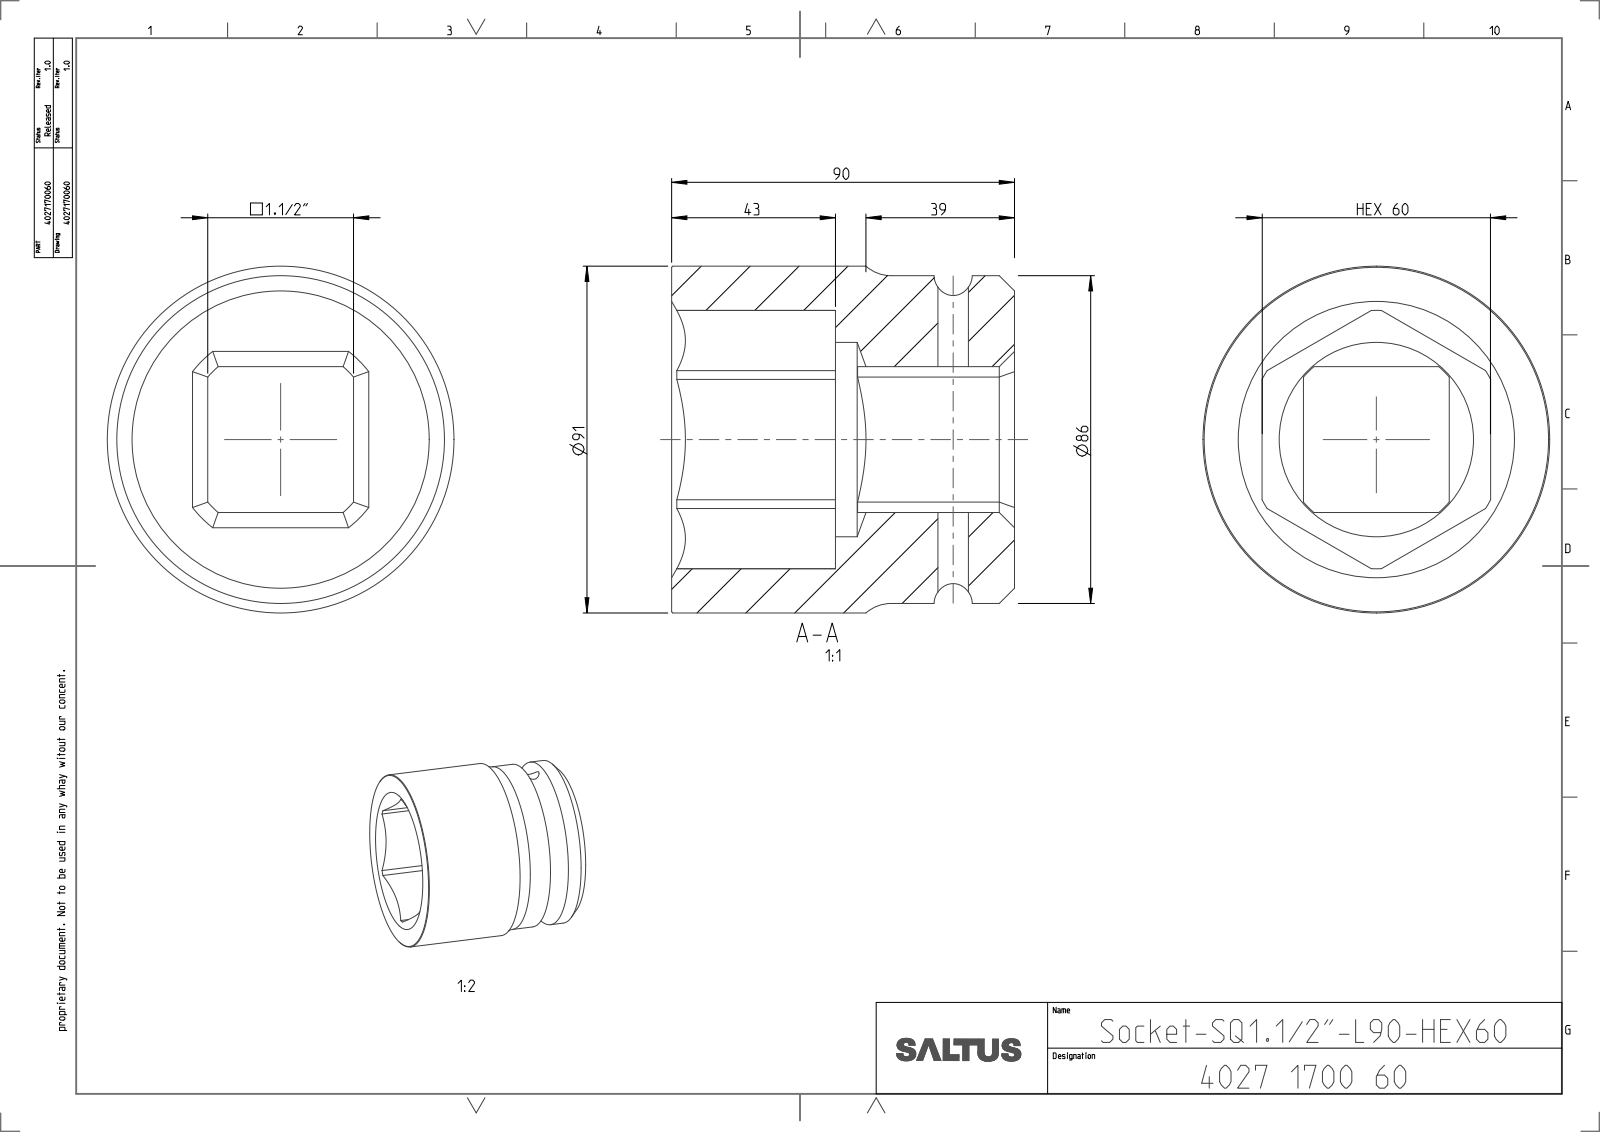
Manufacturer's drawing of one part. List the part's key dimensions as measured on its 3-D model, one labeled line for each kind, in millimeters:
Part name (STEP PRODUCT): 4027170060
STEP written by: CREO PARAMETRIC BY PTC INC, 2022414 (CONFIG_CONTROL_DESIGN)
Units: millimetres
Bodies: 1 solid, 55 faces (17 planar, 22 cylindrical, 16 other)
Overall size (bounding box): 91 × 91 × 90
Volume: 336 946 mm³ · Surface area: 50 947 mm²
Round holes (diameter × count): ⌀8 ×1, ⌀51 ×1
Round bosses / shafts (diameter × count): ⌀91 ×1, ⌀86 ×1
Partial cylindrical surfaces — rounded edges, fillets, slot ends (radius × count): R25.2 ×1, R33.9 ×1
Main face-to-face distances: 60, 10.86, 49.14, 38.28, 90, 47, 43
